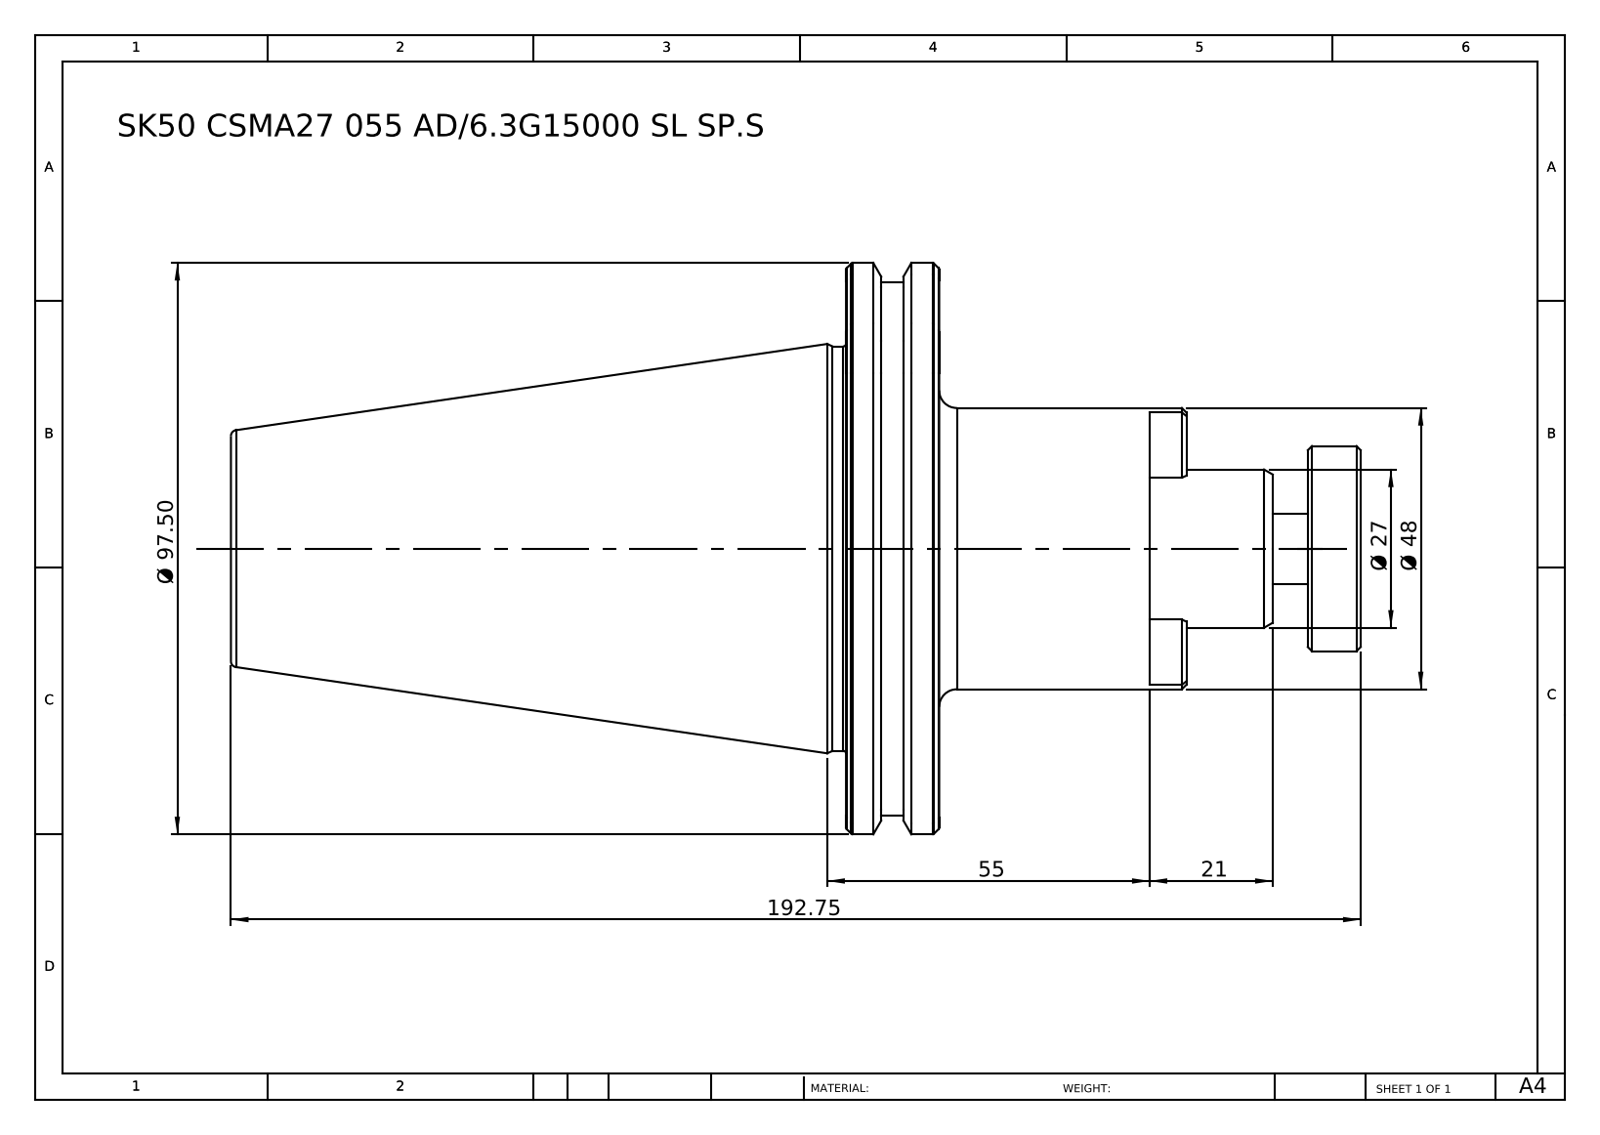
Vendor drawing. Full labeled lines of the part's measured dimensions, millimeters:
Part name (STEP PRODUCT): DRIVER RING -27; SK50 CSMA27 055 AD 6.3G15000 SL SP; SK50 CSMA16 055 MAIN BODY AD-SL -SF
STEP written by: SolidWorks 2014 (CONFIG_CONTROL_DESIGN)
Units: millimetres
Bodies: 2 solids, 125 faces (47 planar, 30 cylindrical, 48 other)
Overall size (bounding box): 192.75 × 97.5 × 93.71
Volume: 455 100 mm³ · Surface area: 50 807 mm²
Round holes (diameter × count): ⌀10 ×1, ⌀27 ×1
Round bosses / shafts (diameter × count): ⌀91 ×1, ⌀69 ×1, ⌀48 ×1, ⌀35 ×1, ⌀12 ×1
Partial cylindrical surfaces — rounded edges, fillets, slot ends (radius × count): R0.8 ×4, R48.75 ×1
Main face-to-face distances: 15.9, 25.9, 41.8, 146.75, 120.85, 104.95, 12, 37.9, 53.8, 158.75
